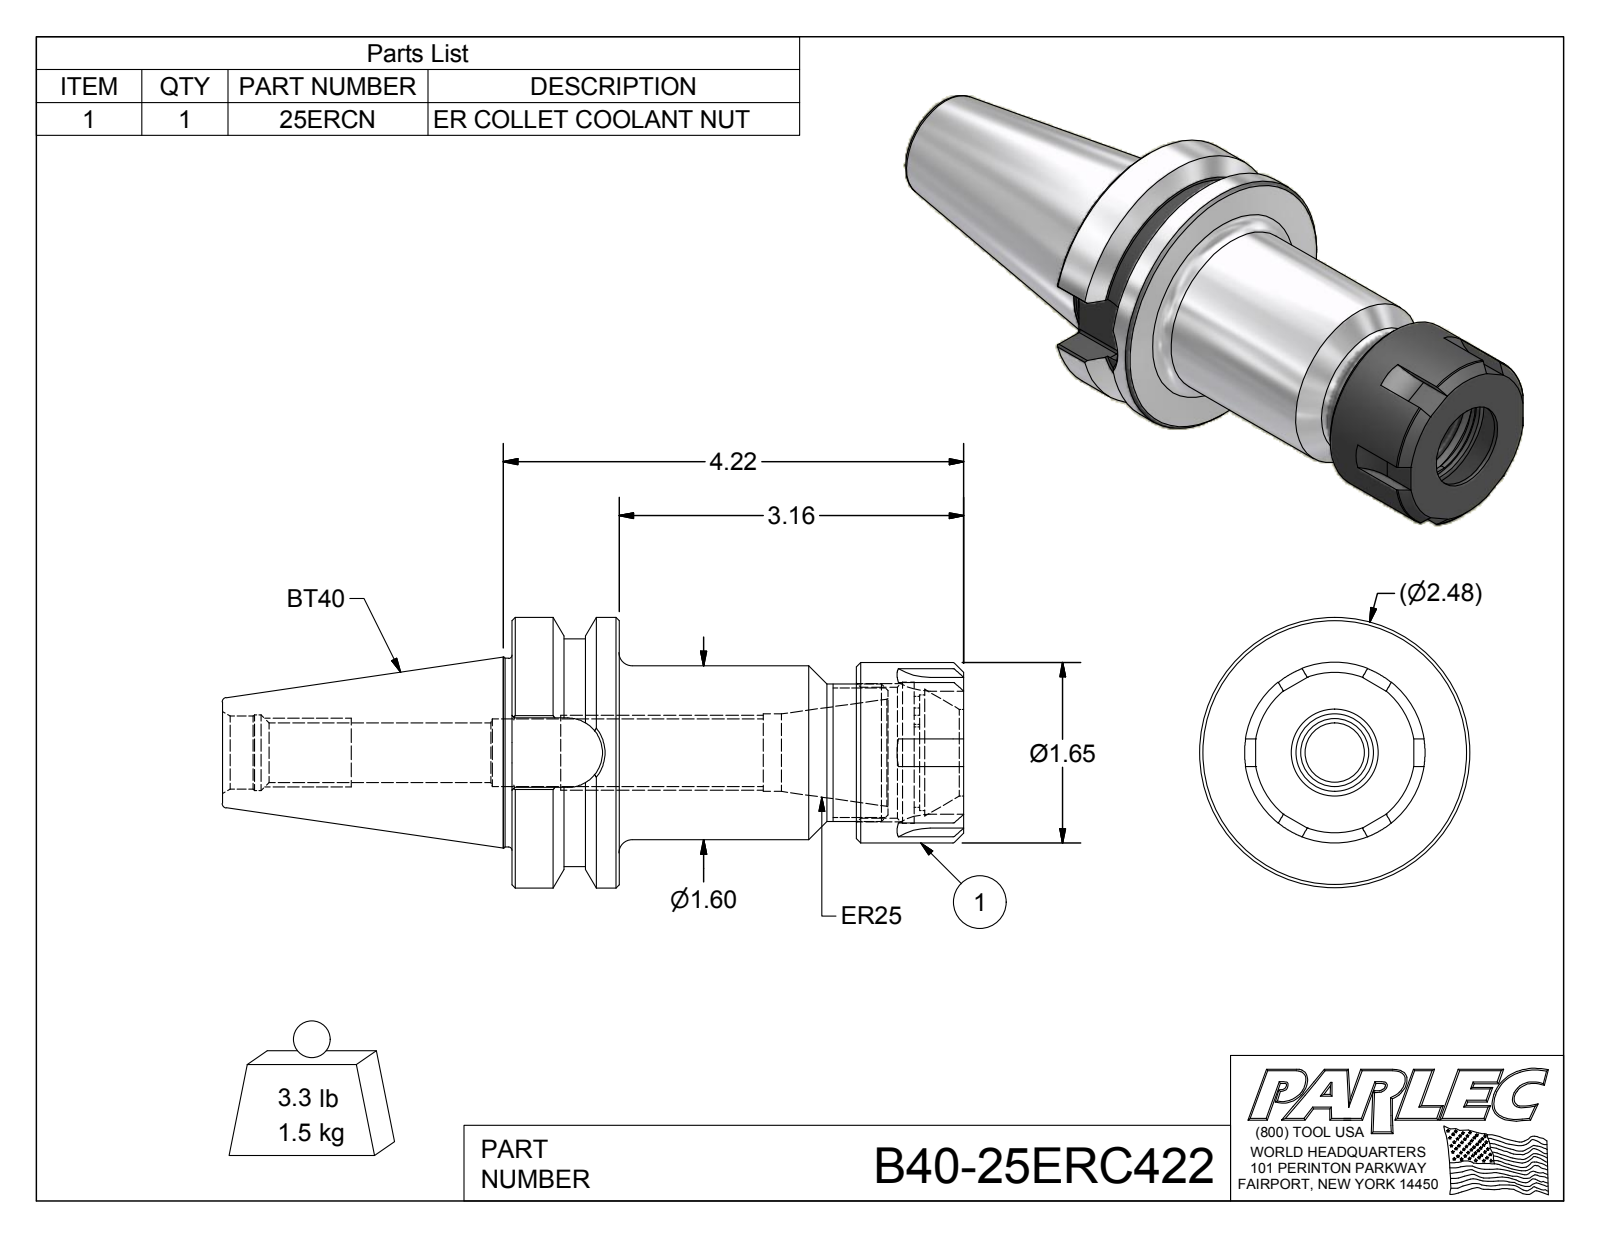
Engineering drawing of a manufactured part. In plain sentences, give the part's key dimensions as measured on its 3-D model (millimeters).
The part is named "B40-25ERC422; B40-25ER4-1; 25ERCN". Its 3-D file was written by "Autodesk Inventor 2012 (AUTOMOTIVE_DESIGN)". It is 2 solids with 131 faces: 52 planar, 39 cylindrical and 40 other. Overall it measures 172.6 by 63 by 63 millimeters. Its volume is 191 200 cubic millimeters and its surface area 40 630 square millimeters. Round holes: 1 of diameter 13.8, 1 of diameter 15.7, 1 of diameter 17, 1 of diameter 17.6, 1 of diameter 18, 1 of diameter 20.2, 1 of diameter 26.8, 1 of diameter 30.5, 1 of diameter 32.9. Round bosses or shafts: 1 of diameter 63, 1 of diameter 53, 1 of diameter 43.9, 1 of diameter 42, 1 of diameter 40.5, 1 of diameter 32. Partial cylindrical surfaces (rounded edges, fillets, slot ends): 8 of radius 0.5, 6 of radius 12.7, 1 of radius 8.1, 1 of radius 12, 1 of radius 13.1. The main face-to-face distances are 25, 105.2, 80.2, 80.2, 55.2, 25, 93.7, 68.7, 13.5, 11.5.
